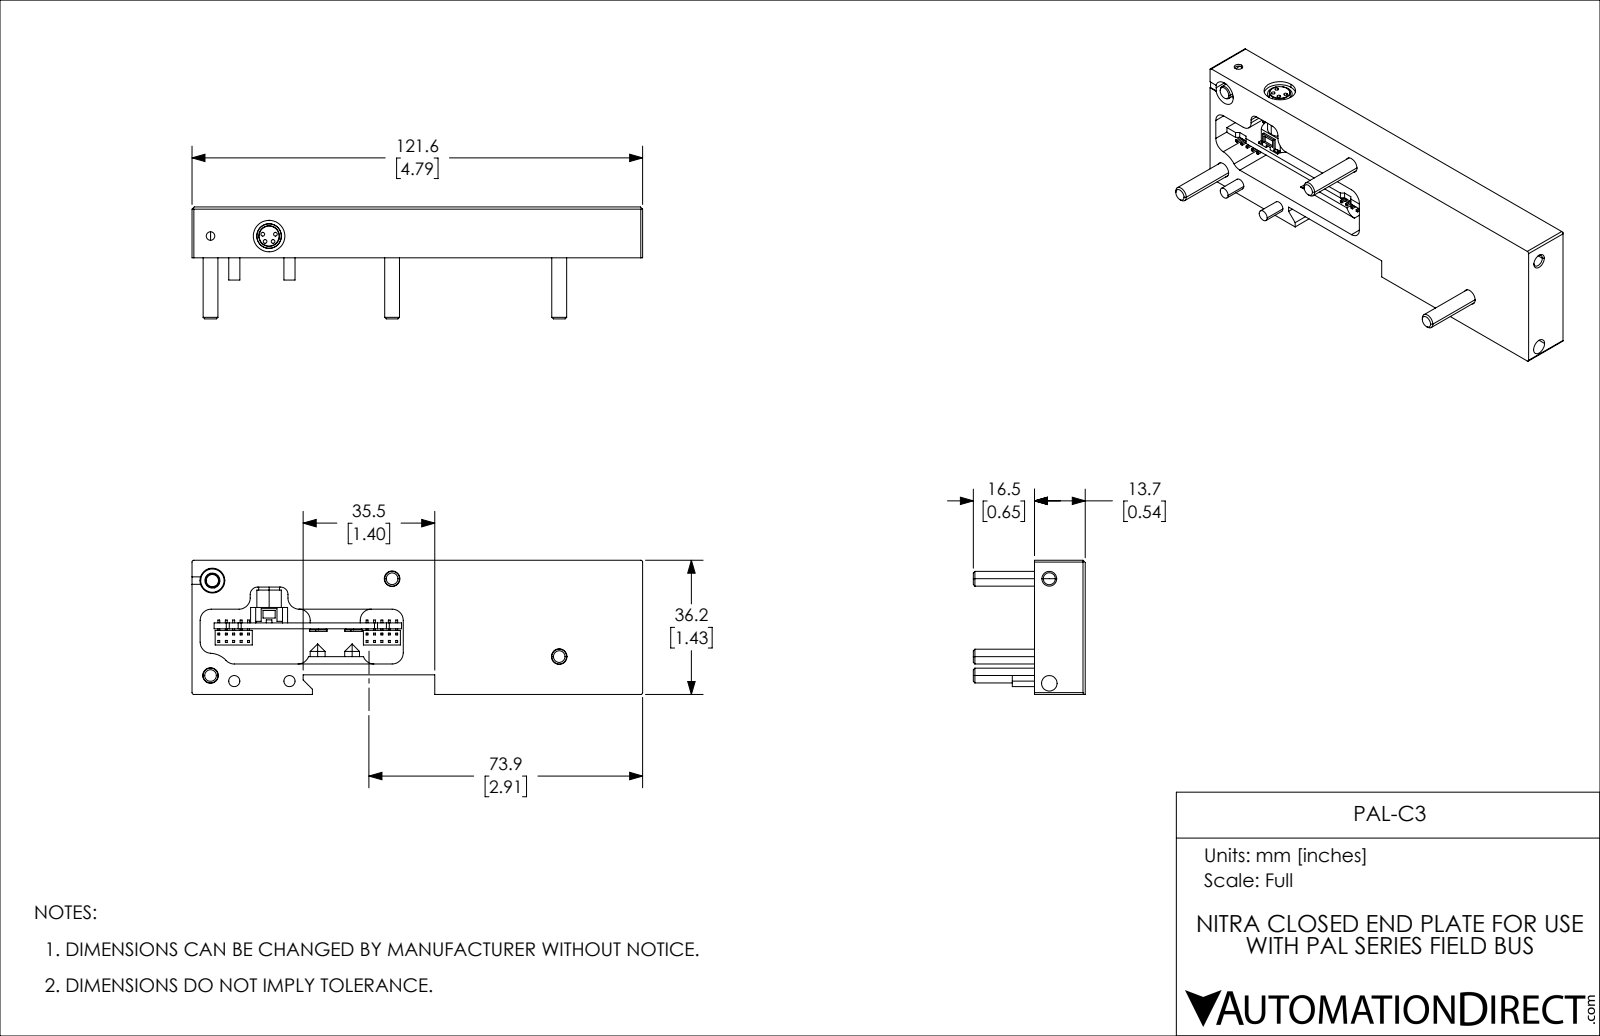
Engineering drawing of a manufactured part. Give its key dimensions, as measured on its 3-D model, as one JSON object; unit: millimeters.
{"part_name": "PAL-C3", "step_written_by": "SolidWorks 2019 (CONFIG_CONTROL_DESIGN)", "units": "millimeters", "bodies": {"solids": 1, "faces": 566, "planar": 404, "cylindrical": 124, "other": 38}, "overall_size": [121.6, 36.2, 30.2], "volume_mm3": 48530, "surface_area_mm2": 20214, "round_holes": [[1, 4], [4.2, 4], [7.5, 3], [0.5, 2], [6.4, 2], [2.3, 1], [3.24, 1], [6.65, 1], [6.7, 1], [7.7, 1], [8.5, 1]], "round_bosses_or_shafts": [[4, 5], [7, 3], [4.7, 2], [3, 2], [6.6, 1], [6.25, 1], [5.6, 1], [3.7, 1]], "partial_cylinders_radius": [[3, 11], [0.5, 4], [0.68, 2], [2, 2], [0.51, 1], [1.02, 1], [3.12, 1], [5, 1]], "face_to_face_distances": [13.7, 36.2, 17.7, 1, 12.7, 5.3, 18.5, 19.3, 1.6, 16.9], "hole_center_spacings": [3.4, 1.77, 1.81, 2.05, 2.99, 4.41, 4.7, 4.8]}
